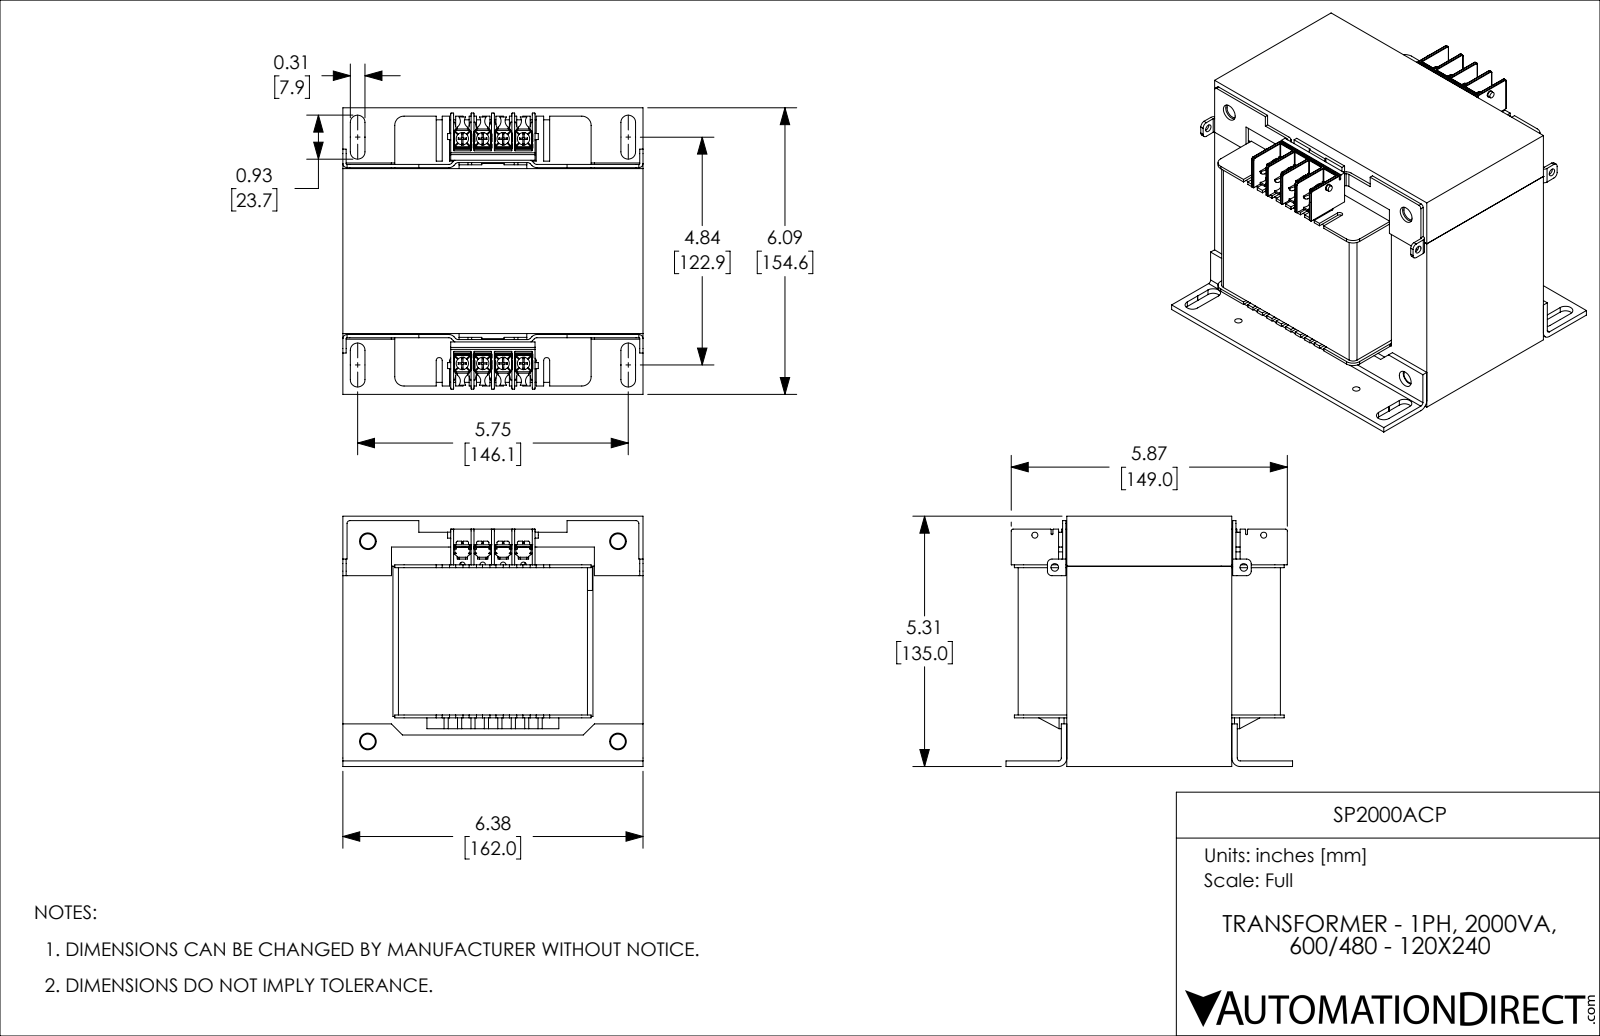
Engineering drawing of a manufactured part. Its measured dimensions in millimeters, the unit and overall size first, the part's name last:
Units: millimetres
Overall size (bounding box): 162 × 154.6 × 135
Round holes (diameter × count): ⌀4 ×13, ⌀2.7 ×8, ⌀3.5 ×8, ⌀8 ×4, ⌀9 ×4, ⌀4.1 ×2, ⌀4.5 ×2
Round bosses / shafts (diameter × count): ⌀6.7 ×8, ⌀6.1 ×8, ⌀4.3 ×8, ⌀2.8 ×8, ⌀3.3 ×2
Partial cylindrical surfaces — rounded edges, fillets, slot ends (radius × count): R0.1 ×52, R0.3 ×52, R0.3 ×34, R0.7 ×32, R4 ×16, R0.9 ×12, R2 ×10, R1.7 ×9
Main face-to-face distances: 108, 27, 132, 135, 3, 89, 105, 54, 30, 24
Hole centre spacings: 11, 22, 121.4, 121.2, 33, 121, 122.9, 121.7
Volume: 2 393 000 mm³ · Surface area: 321 600 mm²
Bodies: 42 solids, 3366 faces (2119 planar, 947 cylindrical, 300 other)
Part name (STEP PRODUCT): SP2000ACP
STEP written by: SolidWorks 2018 (AUTOMOTIVE_DESIGN)
